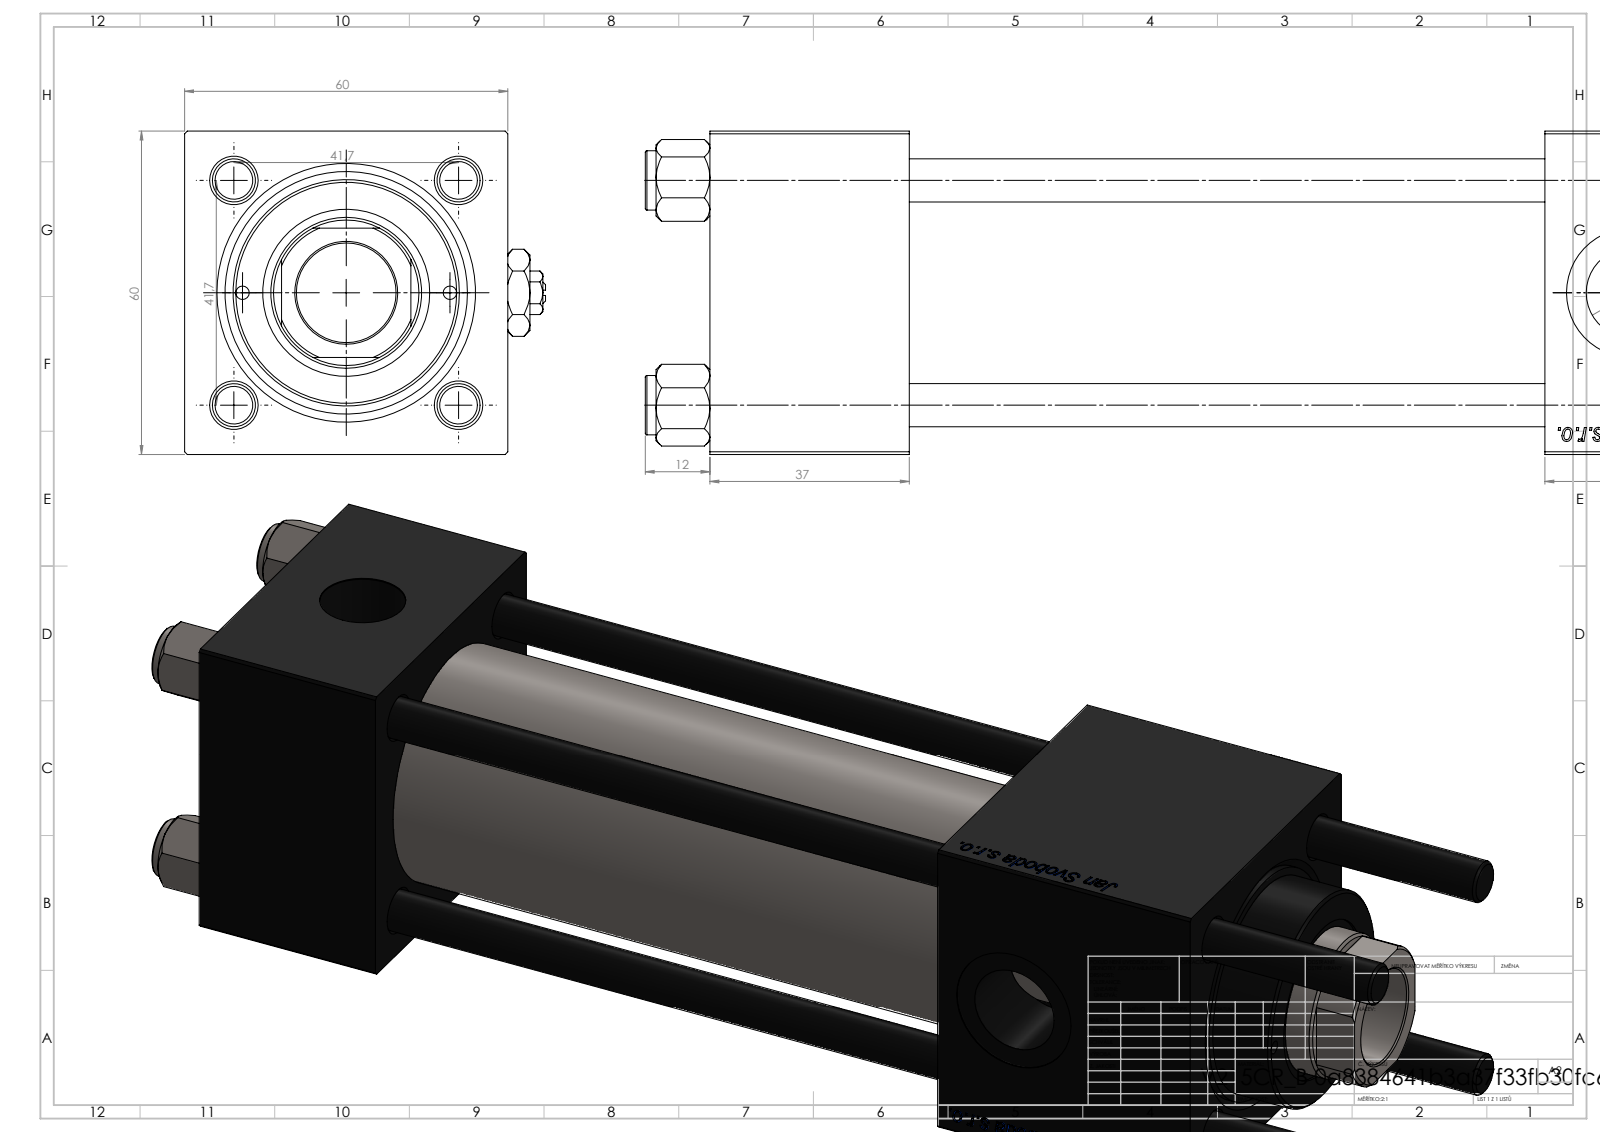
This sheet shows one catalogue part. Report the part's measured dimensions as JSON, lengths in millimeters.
{"part_name": "V215_VC_A; V215CR_B-1; NUT_M5_B; V215CR_VCP_B (+2 more)", "step_written_by": "SolidWorks 2019 (CONFIG_CONTROL_DESIGN)", "units": "millimeters", "bodies": {"solids": 12, "faces": 1213, "planar": 458, "cylindrical": 87, "other": 668}, "overall_size": [255, 67, 60], "volume_mm3": 505901, "surface_area_mm2": 148715, "round_holes": [[8, 4], [2.5, 2], [7, 2], [16.66, 2], [16, 1], [18.5, 1], [24, 1], [28, 1], [31, 1], [40, 1], [45, 1]], "round_bosses_or_shafts": [[11, 4], [46, 1], [42, 1]], "partial_cylinders_radius": [[13.5, 1]], "face_to_face_distances": [60, 37, 155, 118, 179.3, 142.3, 24.3, 53, 208, 171], "hole_center_spacings": [20.91, 29.49, 41.7, 45.2, 19.25, 58.97, 38.5]}
